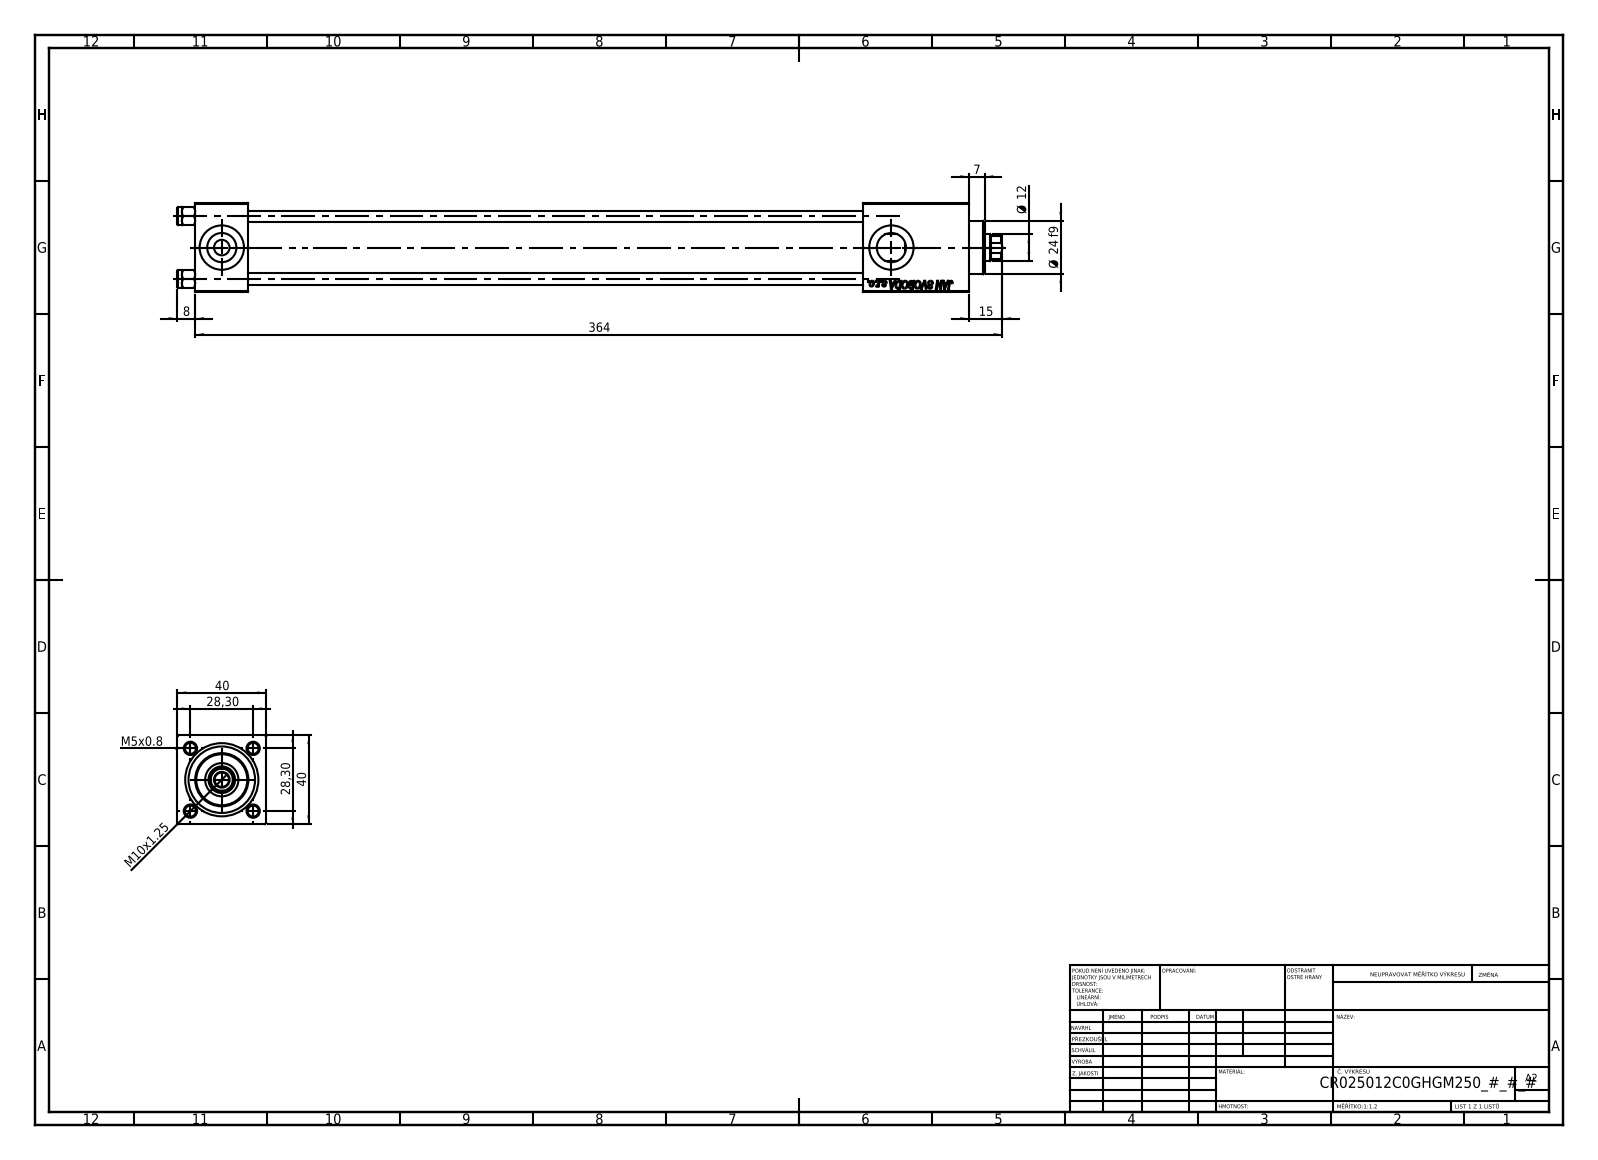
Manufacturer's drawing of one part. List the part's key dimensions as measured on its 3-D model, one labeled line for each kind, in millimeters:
Part name (STEP PRODUCT): V215CR_C_TYCINKA; V215CR_C_Body; V215_VC_A; NUT_M5_C (+1 more)
STEP written by: SolidWorks 2019 (CONFIG_CONTROL_DESIGN)
Units: millimetres
Bodies: 11 solids, 1147 faces (525 planar, 86 cylindrical, 536 other)
Overall size (bounding box): 372 × 40 × 40
Volume: 247 162 mm³ · Surface area: 118 028 mm²
Round holes (diameter × count): ⌀5 ×4, ⌀20 ×3, ⌀7 ×2, ⌀13.16 ×2, ⌀6.5 ×1, ⌀12 ×1, ⌀15 ×1, ⌀25 ×1, ⌀30 ×1
Round bosses / shafts (diameter × count): ⌀8 ×4, ⌀31 ×1, ⌀24 ×1
Partial cylindrical surfaces — rounded edges, fillets, slot ends (radius × count): R5.5 ×1
Main face-to-face distances: 40, 24, 320.3, 296.3, 48, 301, 277, 19.3, 349, 325
Hole centre spacings: 20.01, 28.3, 40.02, 302
